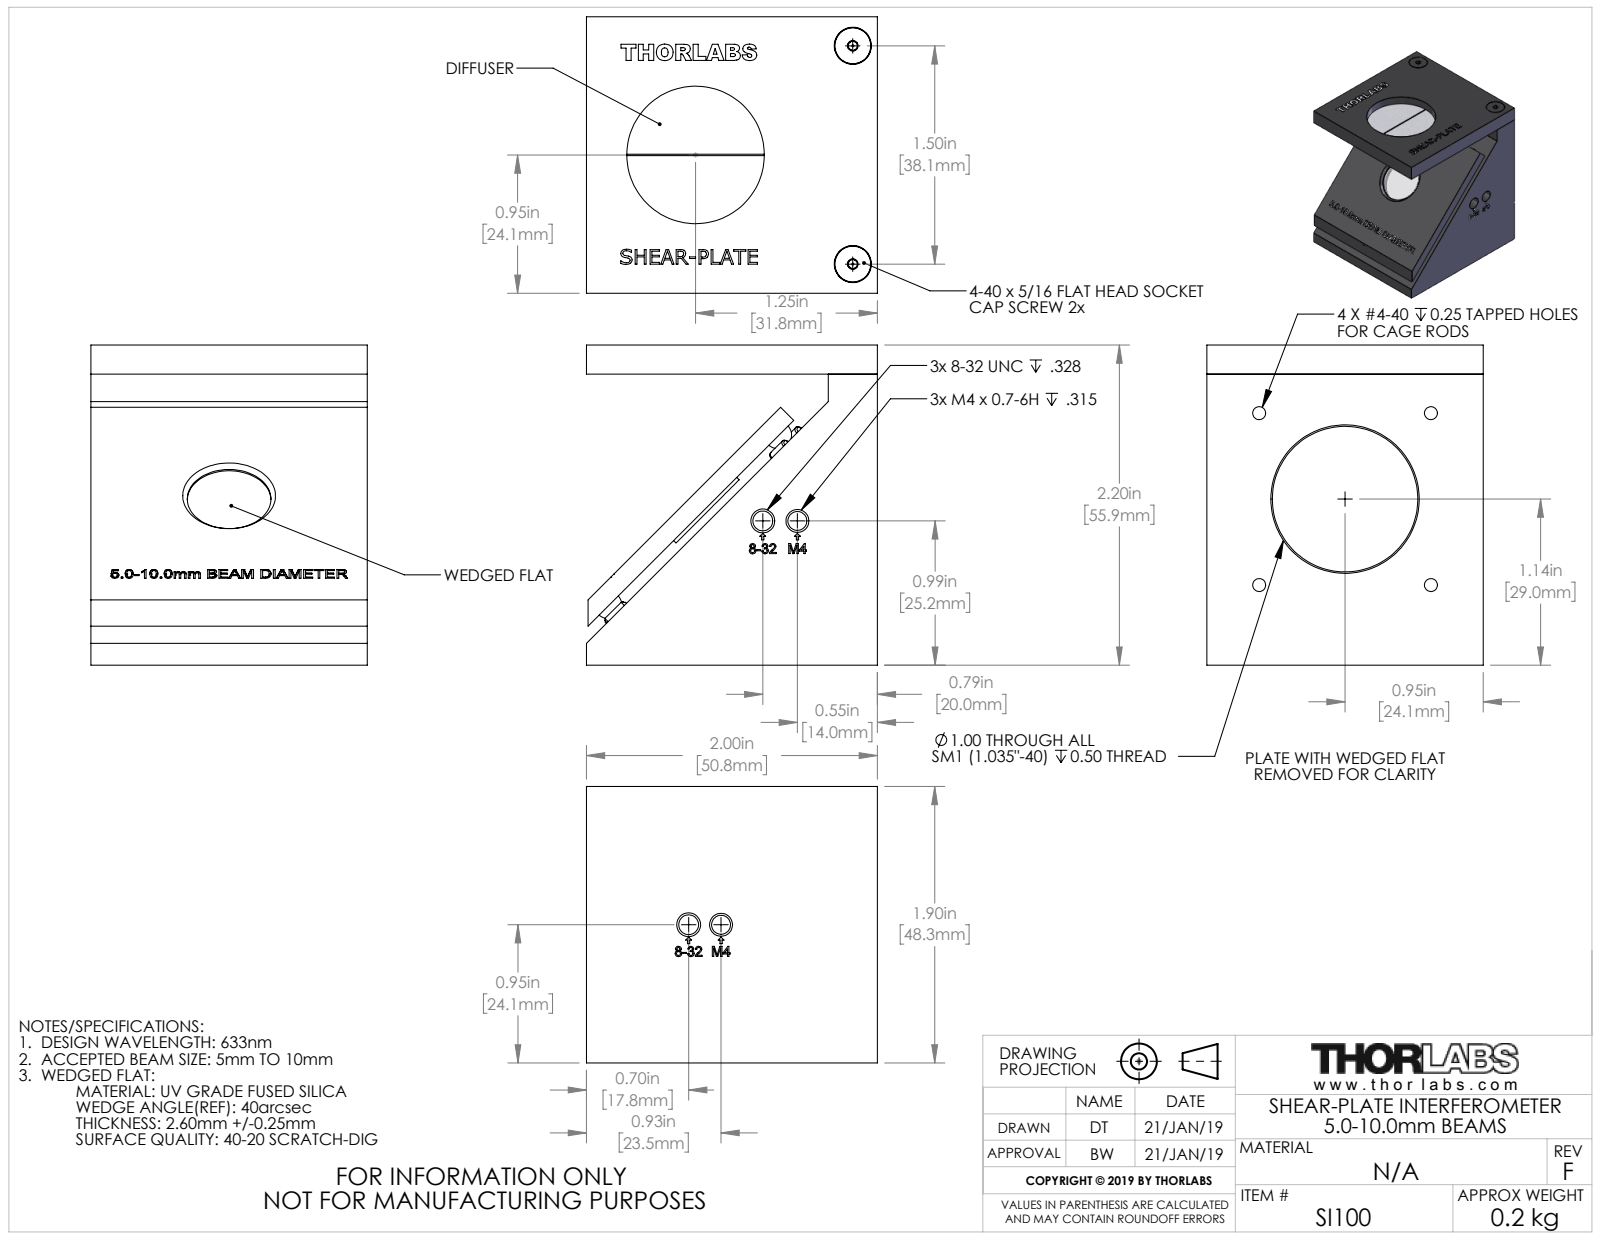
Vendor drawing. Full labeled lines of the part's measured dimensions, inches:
Part name (STEP PRODUCT): 16650-E0W
STEP written by: SolidWorks 2018 (CONFIG_CONTROL_DESIGN)
Units: inches
Bodies: 19 solids, 1141 faces (549 planar, 192 cylindrical, 400 other)
Overall size (bounding box): 2.2 × 2 × 1.9
Volume: 4.54 in³ · Surface area: 42.16 in²
Round holes (diameter × count): ⌀0.089 ×6, ⌀0.063 ×3, ⌀0.124 ×3, ⌀0.136 ×3, ⌀0.142 ×3, ⌀0.164 ×3, ⌀0.187 ×3, ⌀0.129 ×2, ⌀0.13 ×2, ⌀0.157 ×2, ⌀0.575 ×1, ⌀0.615 ×1
Round bosses / shafts (diameter × count): ⌀0.094 ×16, ⌀0.063 ×6, ⌀0.125 ×2, ⌀0.112 ×2, ⌀1 ×1, ⌀0.614 ×1, ⌀0.125 ×1
Partial cylindrical surfaces — rounded edges, fillets, slot ends (radius × count): R0.031 ×12, R0.047 ×4
Main face-to-face distances: 2, 0.128, 2.2, 0.2, 1.9, 0.204, 0.076, 0.343, 0.215, 0.139
Hole centre spacings: 0.835, 0.999, 1.181, 1.4, 1.793, 1, 1.001, 1.176
